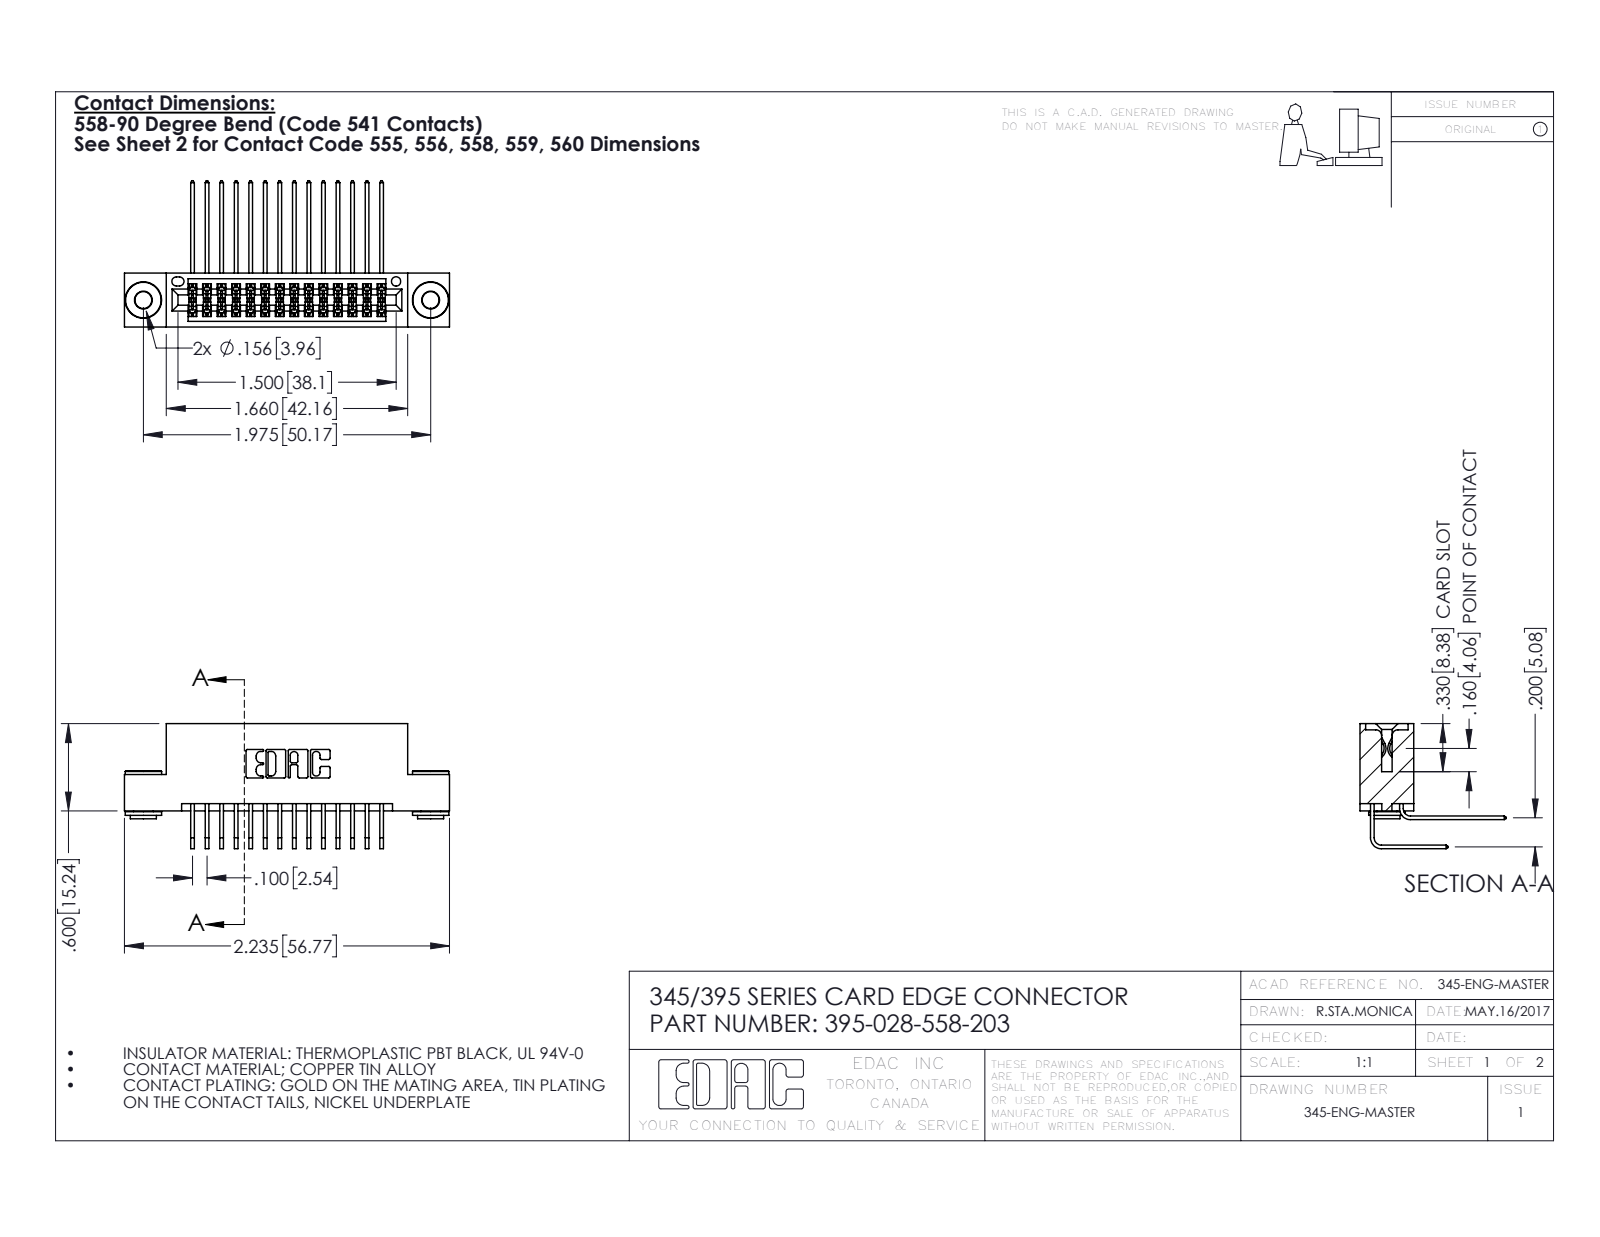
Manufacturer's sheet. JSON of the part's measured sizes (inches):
{"part_name": "345 Part_Flush Mounting Lugs - 0.156 Dia-TH; 345-292-001_558 559 Tail - 1; 345-292-001_558 Tail - 2; 395-028-558-203 (+1 more)", "step_written_by": "SolidWorks 2016 (CONFIG_CONTROL_DESIGN)", "units": "inches", "bodies": {"solids": 31, "faces": 1620, "planar": 1070, "cylindrical": 542, "other": 8}, "overall_size": [2.235, 1.005, 0.859], "volume_in3": 0.332, "surface_area_in2": 13.11, "round_holes": [[0.116, 2], [0.156, 2], [0.064, 1]], "round_bosses_or_shafts": [[0.25, 2], [0.18, 2], [0.136, 2]], "partial_cylinders_radius": [[0.006, 43], [0.01, 22], [0.007, 6], [0.031, 6], [0.026, 3], [0.014, 2], [0.019, 2], [0.022, 2]], "face_to_face_distances": [0.2, 0.072, 0.298, 0.37, 0.025, 0.098, 0.272, 0.225, 0.285, 0.025], "hole_center_spacings": [0.27, 1.742, 1.975]}
